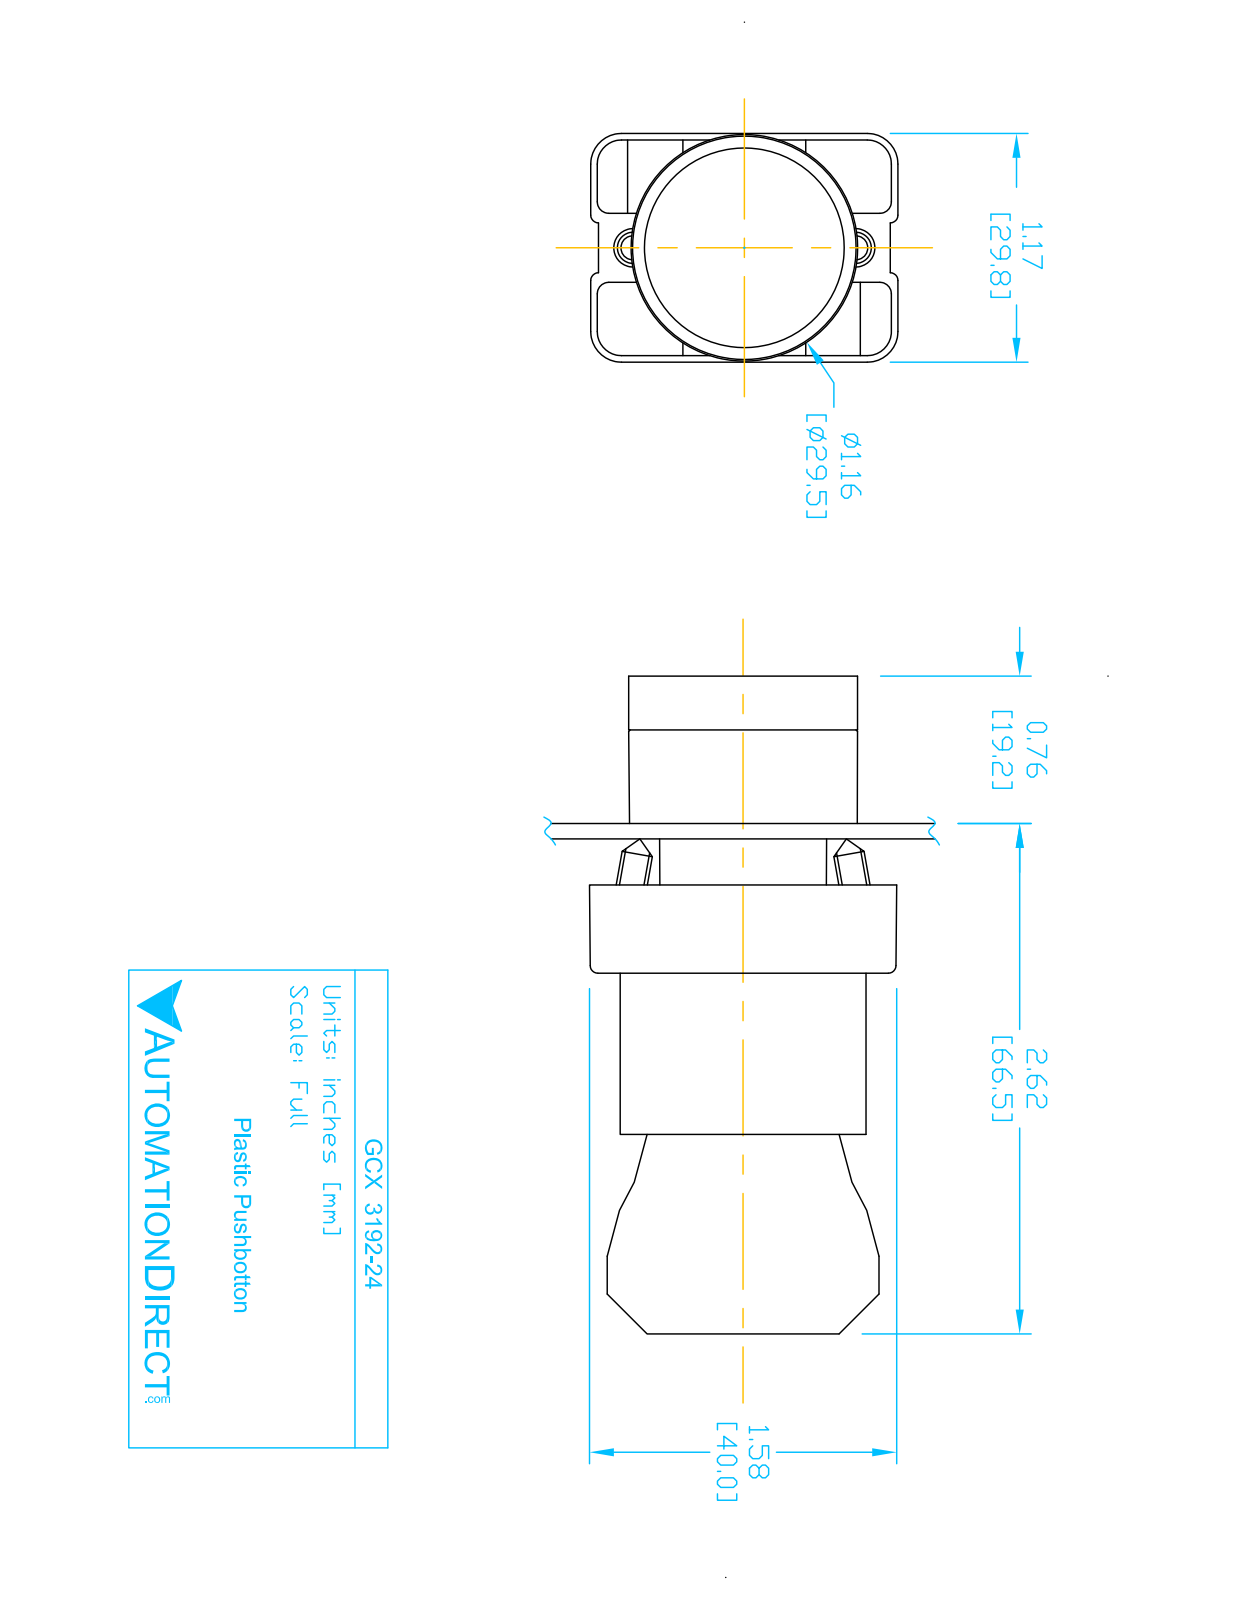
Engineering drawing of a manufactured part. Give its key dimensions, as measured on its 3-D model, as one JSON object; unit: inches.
{"part_name": "ECX1050; CONTACT BLOCK; ECX3029-2; GCX3192-24 (+1 more)", "step_written_by": "SolidWorks 2016 (AUTOMOTIVE_DESIGN)", "units": "inches", "bodies": {"solids": 8, "faces": 431, "planar": 252, "cylindrical": 148, "other": 31}, "overall_size": [3.319, 1.581, 1.177], "volume_in3": 2.794, "surface_area_in2": 38.77, "round_holes": [[0.079, 2], [0.124, 2], [0.13, 2], [0.087, 1], [0.197, 1], [0.469, 1], [0.878, 1], [0.888, 1], [1.024, 1]], "round_bosses_or_shafts": [[0.157, 4], [1.175, 1], [1.004, 1], [0.945, 1], [0.856, 1], [0.78, 1], [0.504, 1]], "partial_cylinders_radius": [[0.059, 24], [0.041, 12], [0.124, 12], [0.157, 12], [0.039, 8], [0.128, 2], [0.02, 1], [0.063, 1]], "face_to_face_distances": [0.827, 0.579, 2.02, 1.193, 1.171, 0.276, 2.295, 1.469, 0.031, 0.033], "hole_center_spacings": [0.236, 0.544, 0.472, 0.49]}
